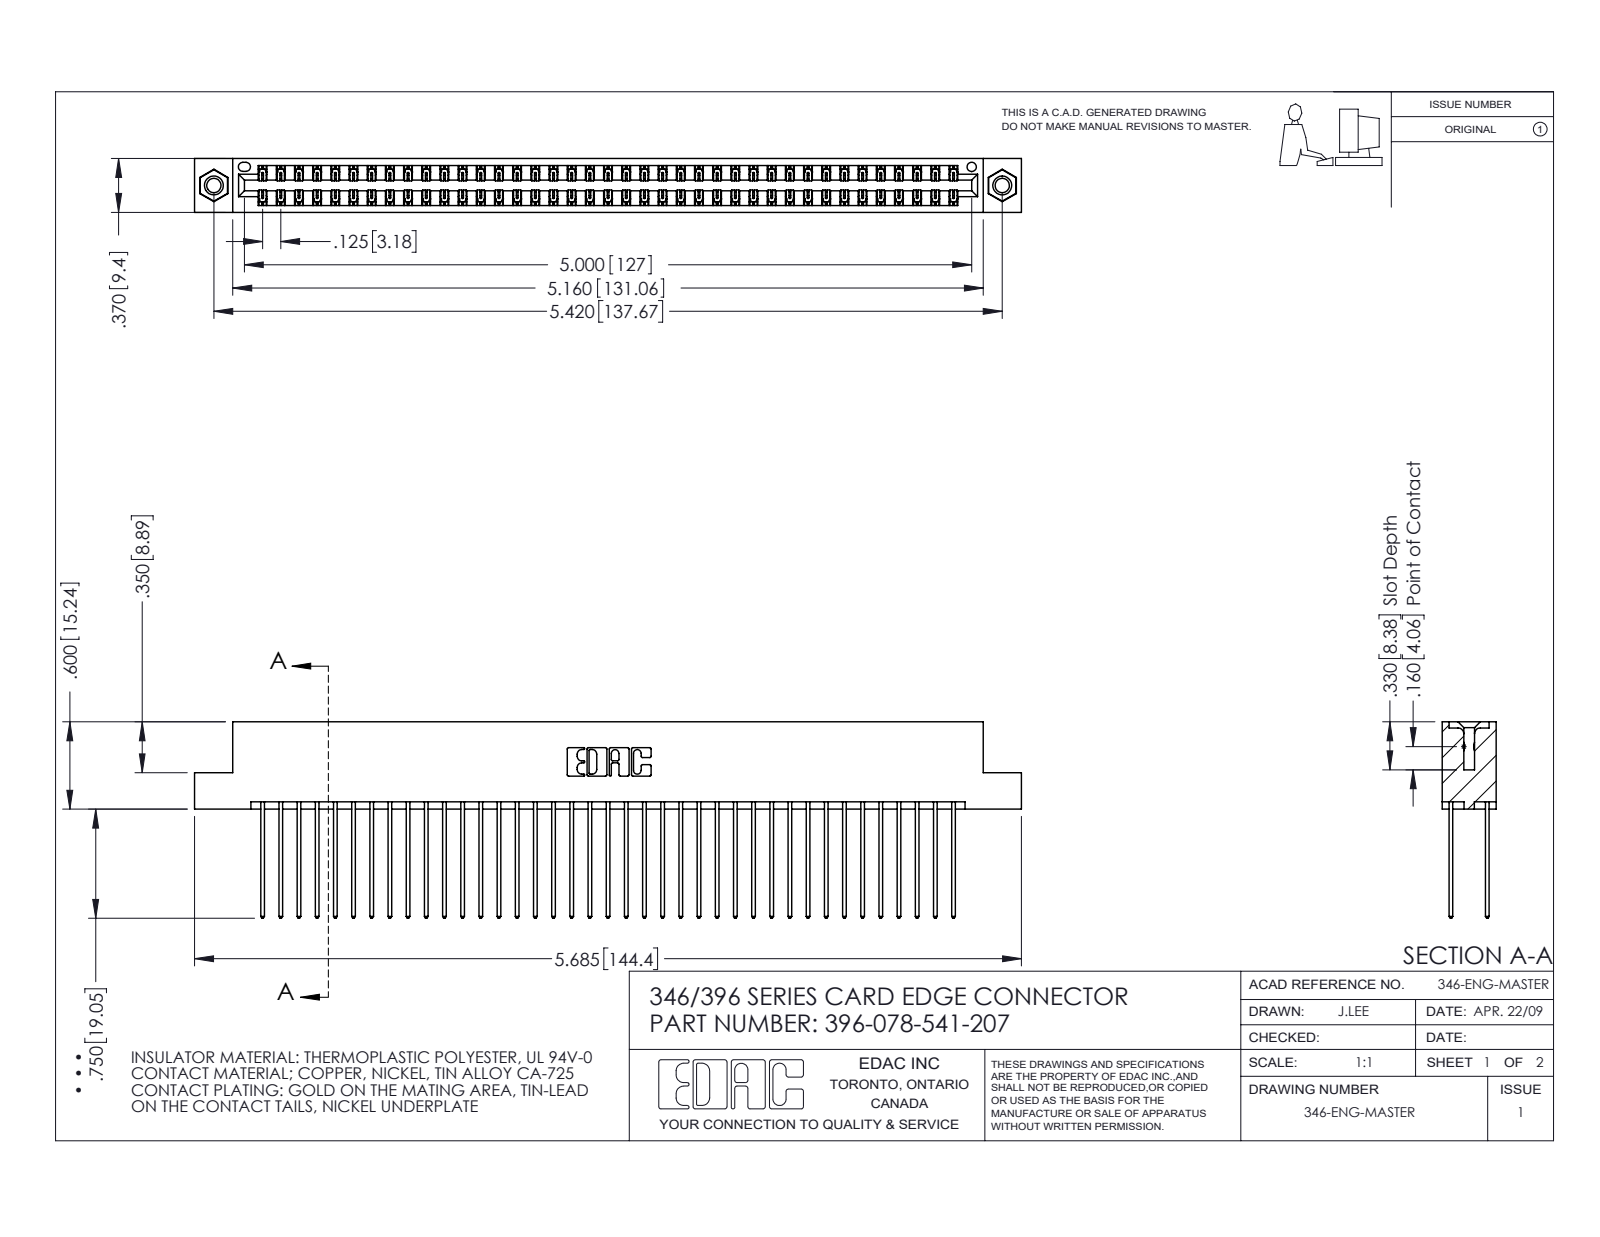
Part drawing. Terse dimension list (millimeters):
name: 345-250-001_345-250-005-103; 346 Part_Flush Mounting Lugs - 0.156 Dia-TI; 345-292-001_345-293-141; 396-078-541-207
written by: SolidWorks 2016 (CONFIG_CONTROL_DESIGN)
unit: mm
bodies: 81 solids, 4238 faces (2838 planar, 1384 cylindrical, 16 other)
size: 144.4 × 34.3 × 9.4
volume: 14 500 mm³; area: 22 050 mm²
holes: 2× ⌀2.5, 2× ⌀3.2, 2× ⌀4, 1× ⌀1.6
bosses: 2× ⌀3.9
rounds: 117× R0.2, 78× R0.3, 22× R0.3, 6× R0.2, 6× R0.8, 3× R0.7, 2× R0.4, 2× R0.6
face distances: 1.2, 8.2, 6.4, 1.8, 7.6, 0.6, 9.4, 7, 5.7, 3.8
hole spacings: 6.2, 132.4, 137.7
